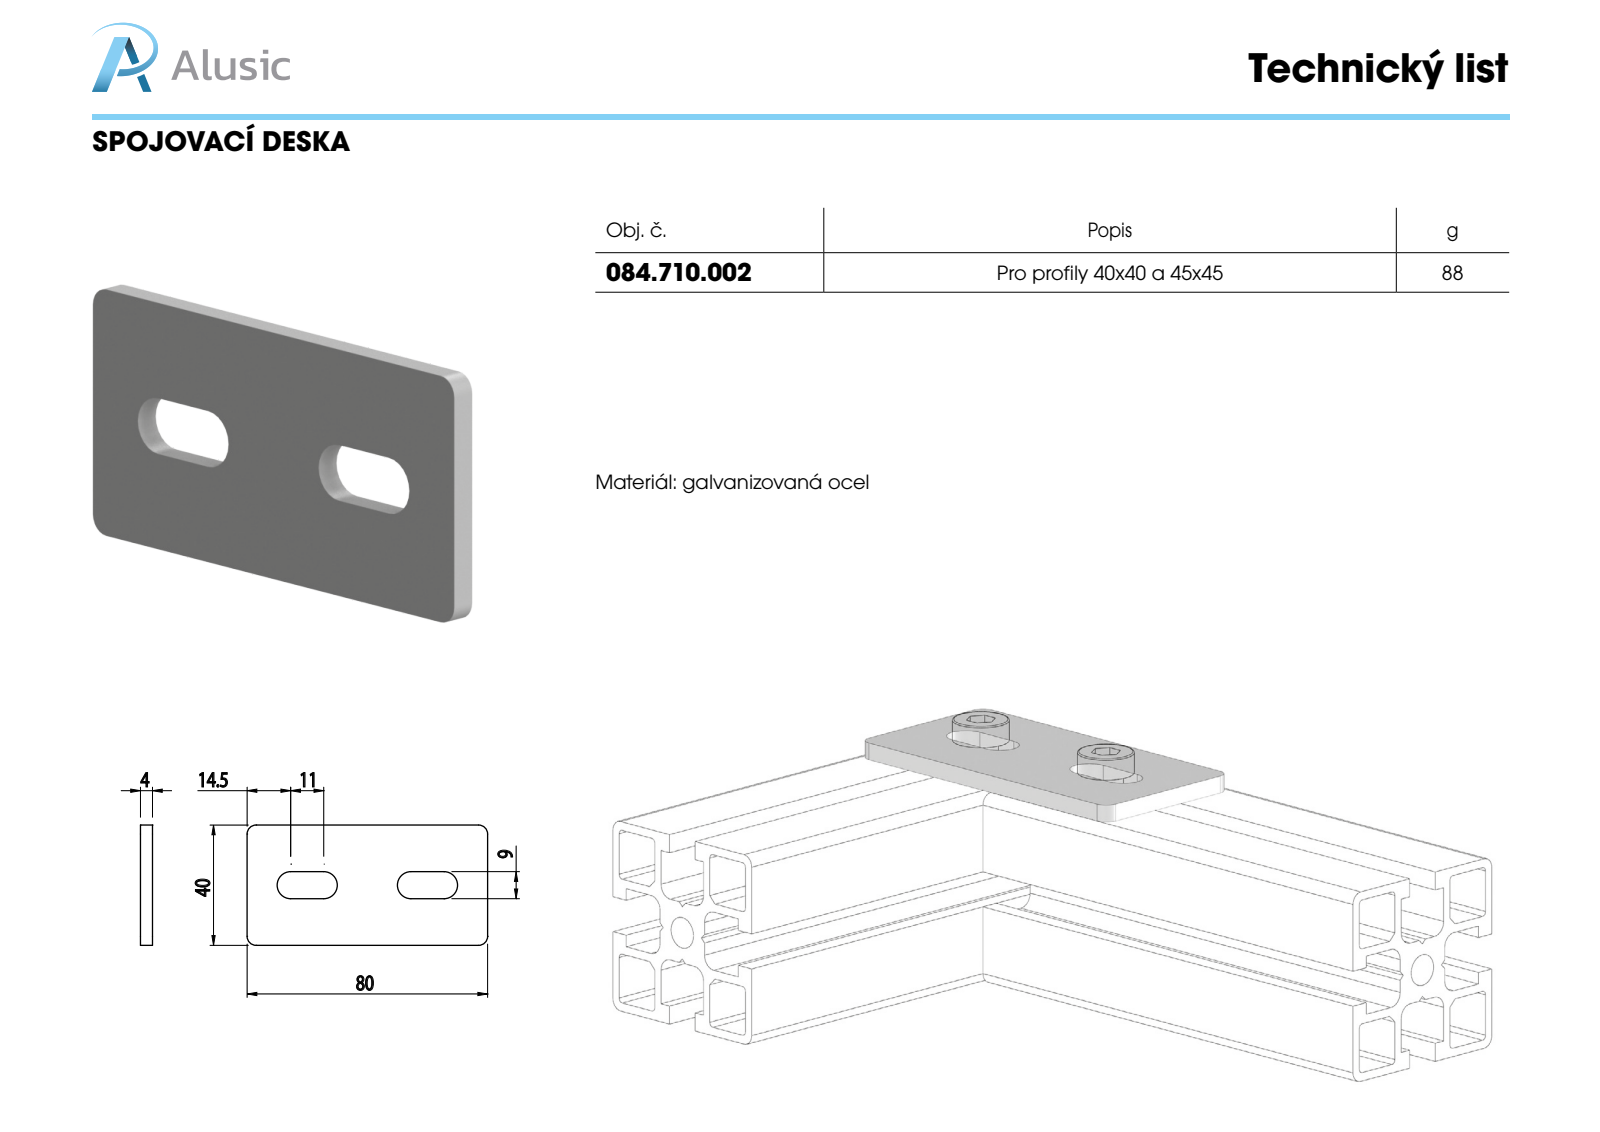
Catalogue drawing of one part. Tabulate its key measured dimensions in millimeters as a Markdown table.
| quantity | value |
| --- | --- |
| part name | 084.710.002 |
| STEP written by | SolidWorks 2011 (CONFIG_CONTROL_DESIGN) |
| units | millimeters |
| bodies | 1 solid, 18 faces (10 planar, 8 cylindrical, 0 other) |
| overall size | 80 × 40 × 4 |
| volume | 11 468 mm³ |
| surface area | 7 076 mm² |
| partial cylindrical surfaces (radius × count) | 3 × 4, 4.5 × 4 |
| main face-to-face distances | 4, 40, 15.5, 24.5, 80, 9 |
